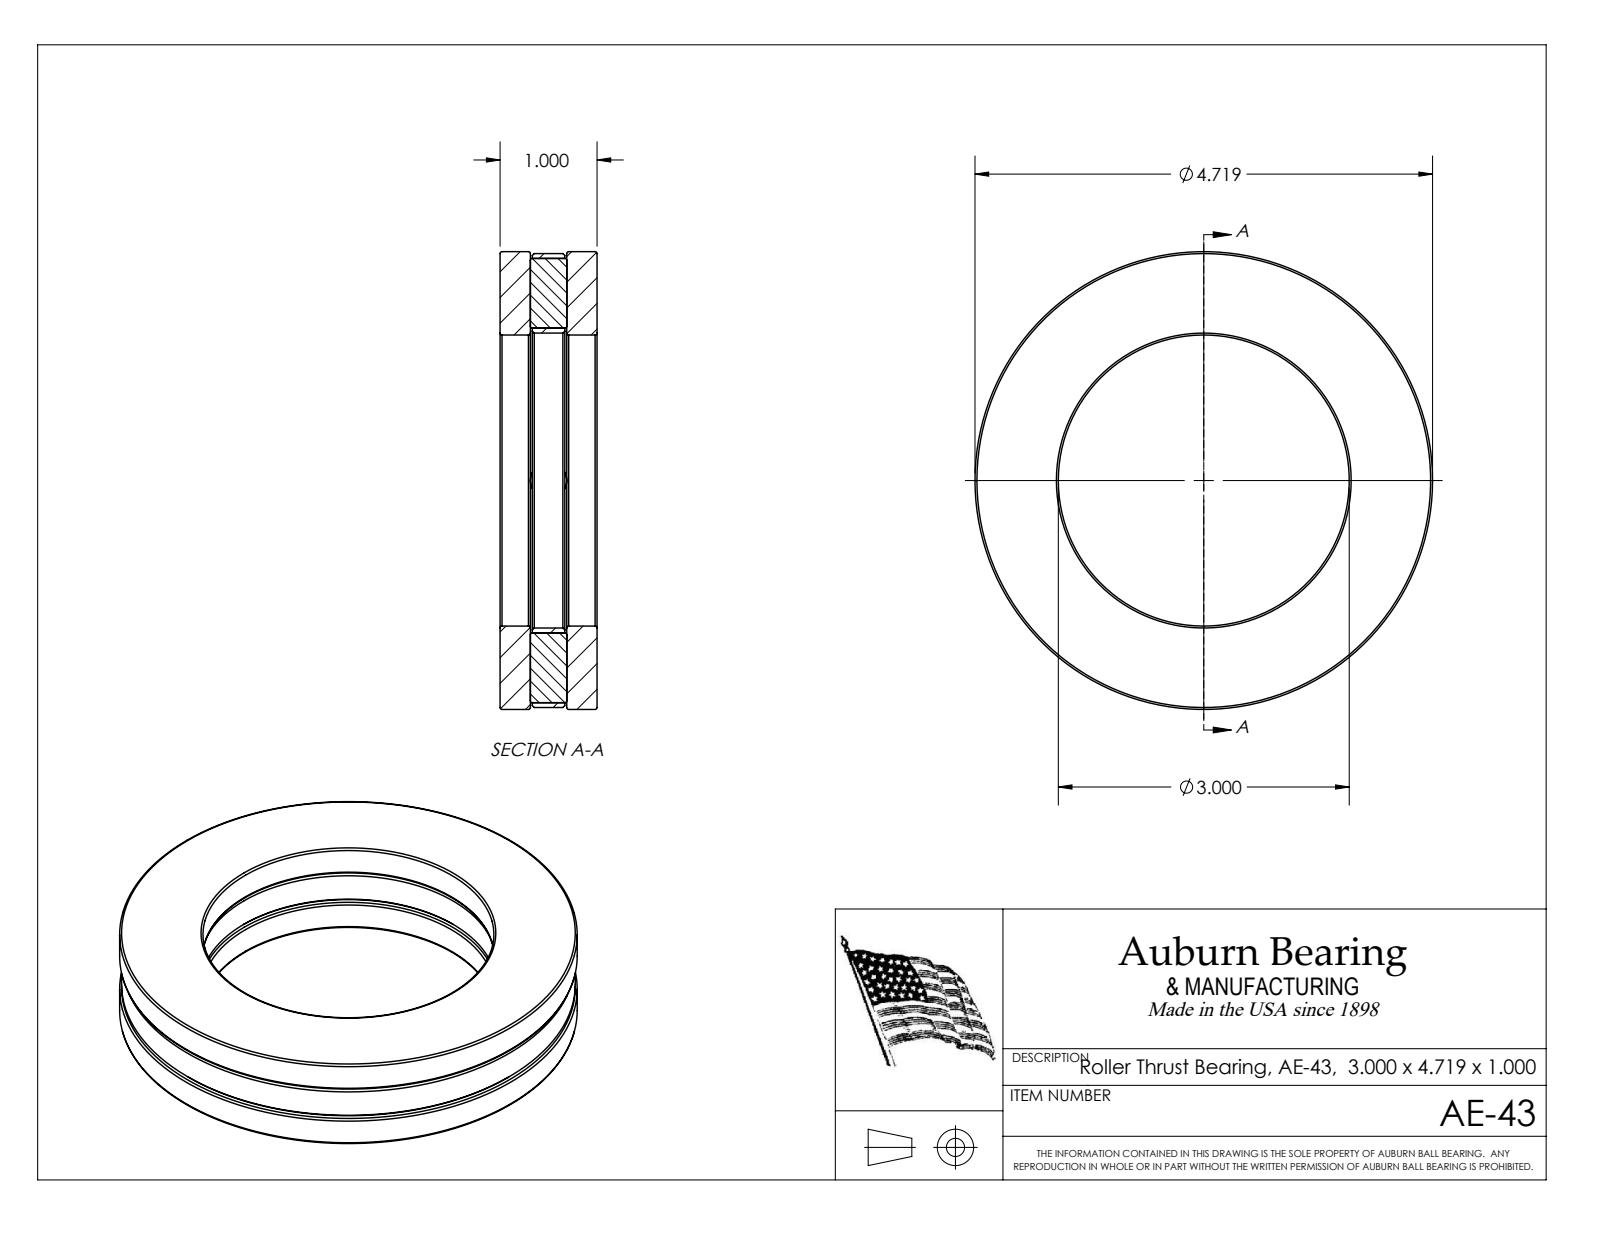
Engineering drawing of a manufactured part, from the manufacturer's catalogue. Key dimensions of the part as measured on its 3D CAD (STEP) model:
Part name (STEP PRODUCT): AE-43
STEP written by: SolidWorks 2017 (CONFIG_CONTROL_DESIGN)
Units: inches
Bodies: 7 solids, 60 faces (30 planar, 10 cylindrical, 20 other)
Overall size (bounding box): 4.719 × 4.719 × 1
Volume: 9.778 in³ · Surface area: 88.39 in²
Round holes (diameter × count): ⌀3 ×1, ⌀3.04 ×1
Round bosses / shafts (diameter × count): ⌀0.375 ×2, ⌀4.719 ×1, ⌀4.679 ×1
Main face-to-face distances: 0.313, 0.687, 0.333, 0.667, 0.02, 0.355, 0.375, 1, 0.335, 1.383
